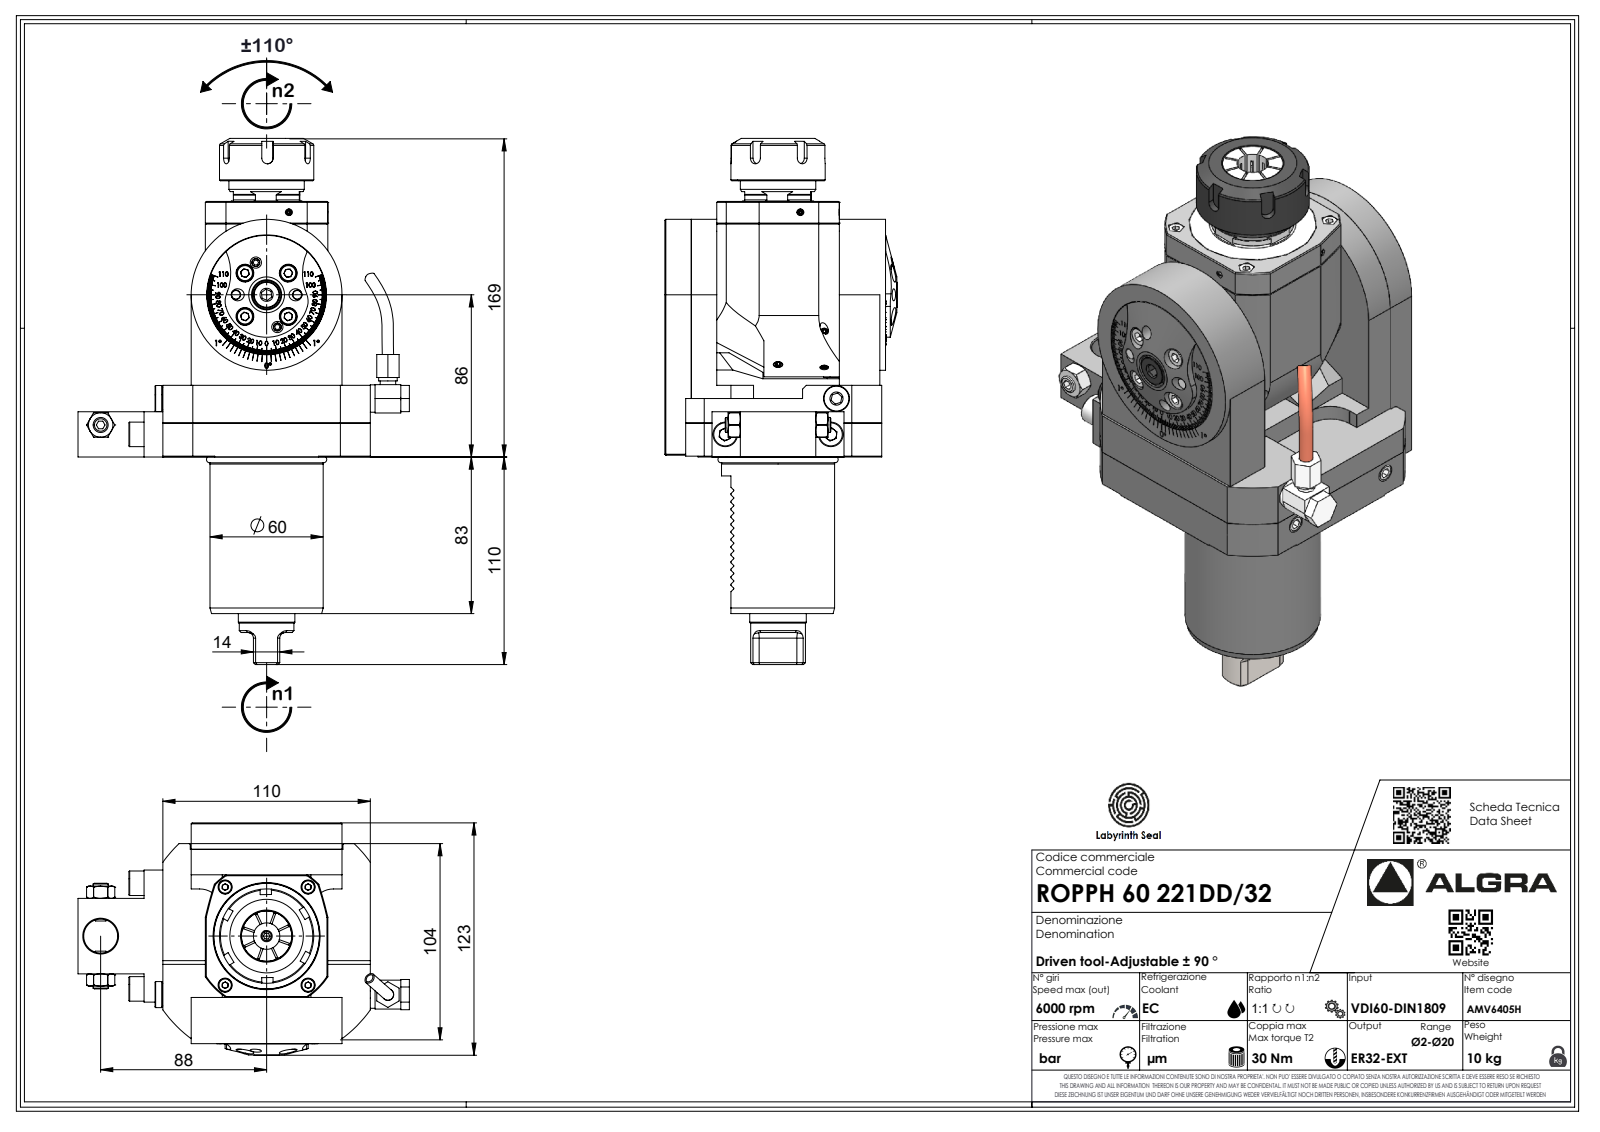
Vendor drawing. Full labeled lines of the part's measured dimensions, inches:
Part name (STEP PRODUCT): ROPPH60221DD32
STEP written by: SolidWorks 2023 (AUTOMOTIVE_DESIGN)
Units: inches
Bodies: 1 solid, 693 faces (437 planar, 115 cylindrical, 141 other)
Overall size (bounding box): 10.981 × 6.917 × 4.843
Volume: 89.16 in³ · Surface area: 201.9 in²
Round holes (diameter × count): ⌀0.083 ×1, ⌀0.197 ×1, ⌀1.74 ×1, ⌀1.898 ×1, ⌀2.055 ×1, ⌀2.213 ×1
Round bosses / shafts (diameter × count): ⌀3.15 ×1, ⌀2.362 ×1, ⌀2.311 ×1, ⌀2.205 ×1, ⌀2.047 ×1, ⌀1.969 ×1, ⌀1.89 ×1, ⌀1.732 ×1
Partial cylindrical surfaces — rounded edges, fillets, slot ends (radius × count): R0.012 ×14, R0.118 ×11, R0.013 ×7, R0.02 ×7, R0.146 ×7, R0.008 ×3, R0.394 ×2, R0.472 ×2
Main face-to-face distances: 0.886, 3.445, 2.559, 0.276, 3.15, 0.295, 1.083, 0.591, 2.854, 3.74
